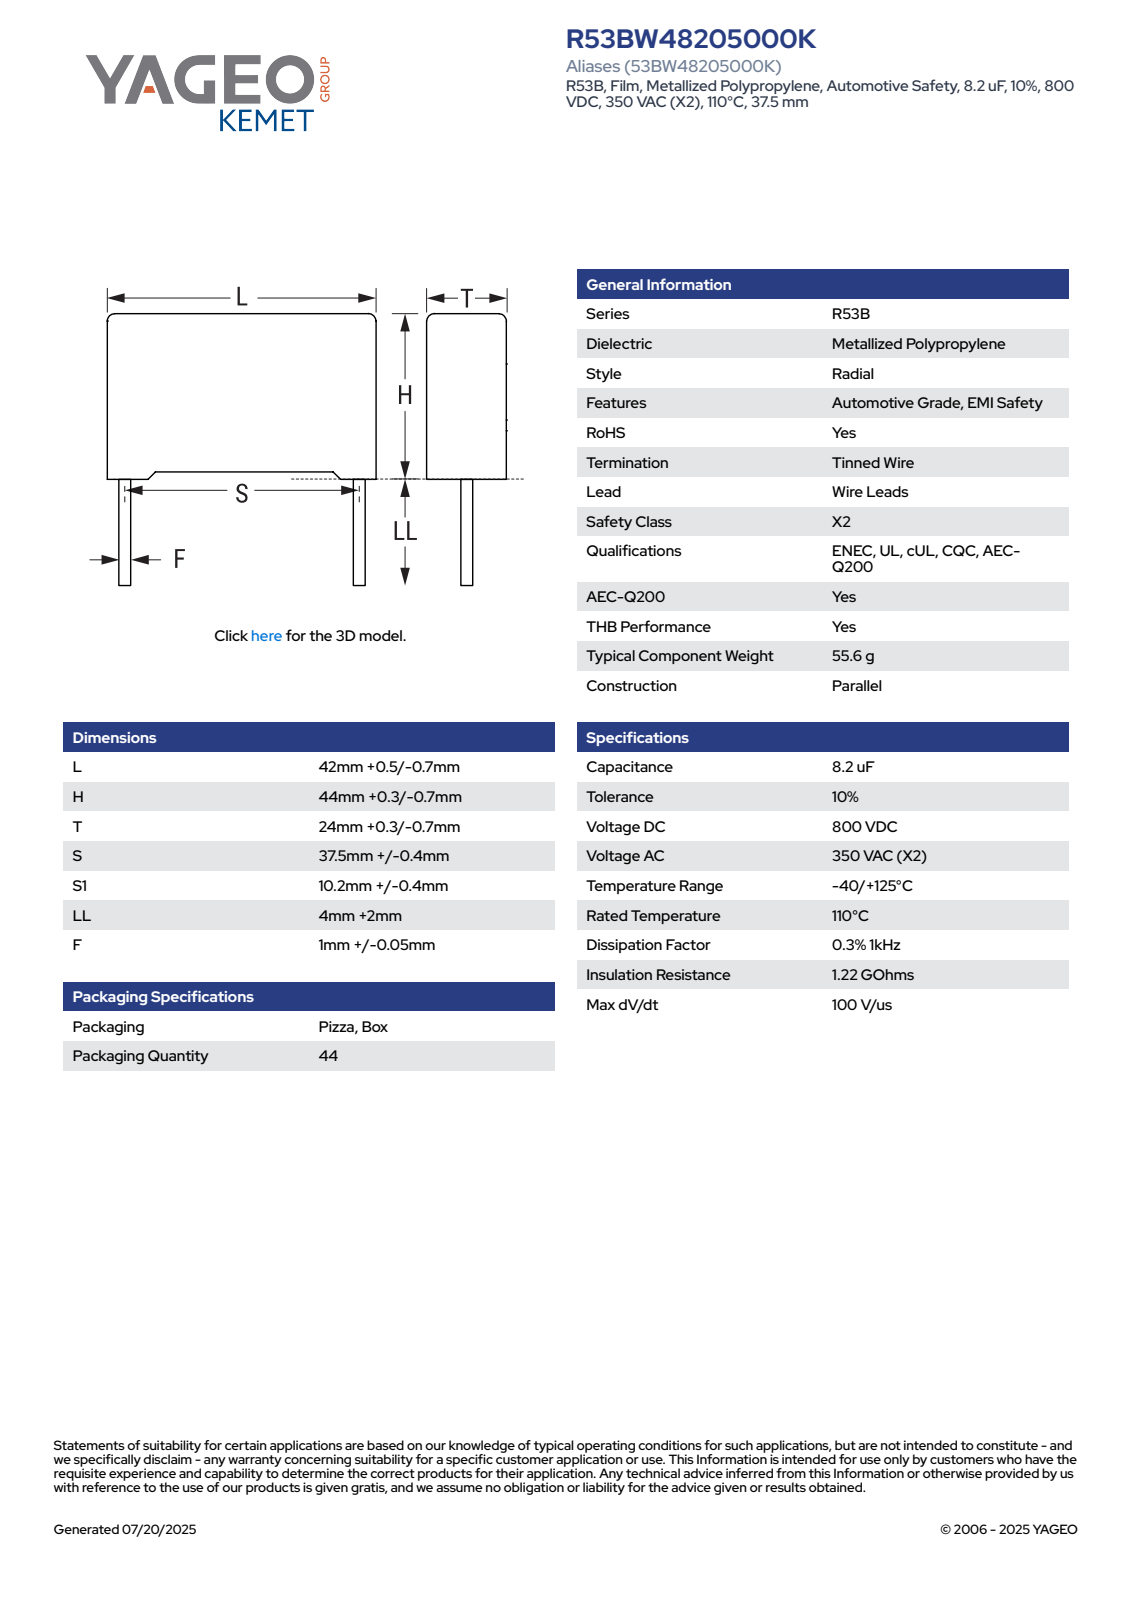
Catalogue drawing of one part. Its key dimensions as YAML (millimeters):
part_name: "CFR_RB2_42X44X24_L42.5H44.3T24.3S37.5LL6F1.05"
step_written_by: "SolidWorks 2021 (AUTOMOTIVE_DESIGN)"
units: millimeters
bodies: {solids: 4, faces: 85, planar: 77, cylindrical: 8, other: 0}
overall_size: [50.3, 42.5, 24.3]
volume: 44426
surface_area: 8095
round_bosses_or_shafts:
  - {diameter: 1.05, count: 2}
partial_cylinders:
  - {radius: 0.5, count: 4}
face_to_face_distances: [24.3, 42.5, 42.77, 0.78, 43.55, 0.75, 1.53, 44.3, 1.42, 24.31]
